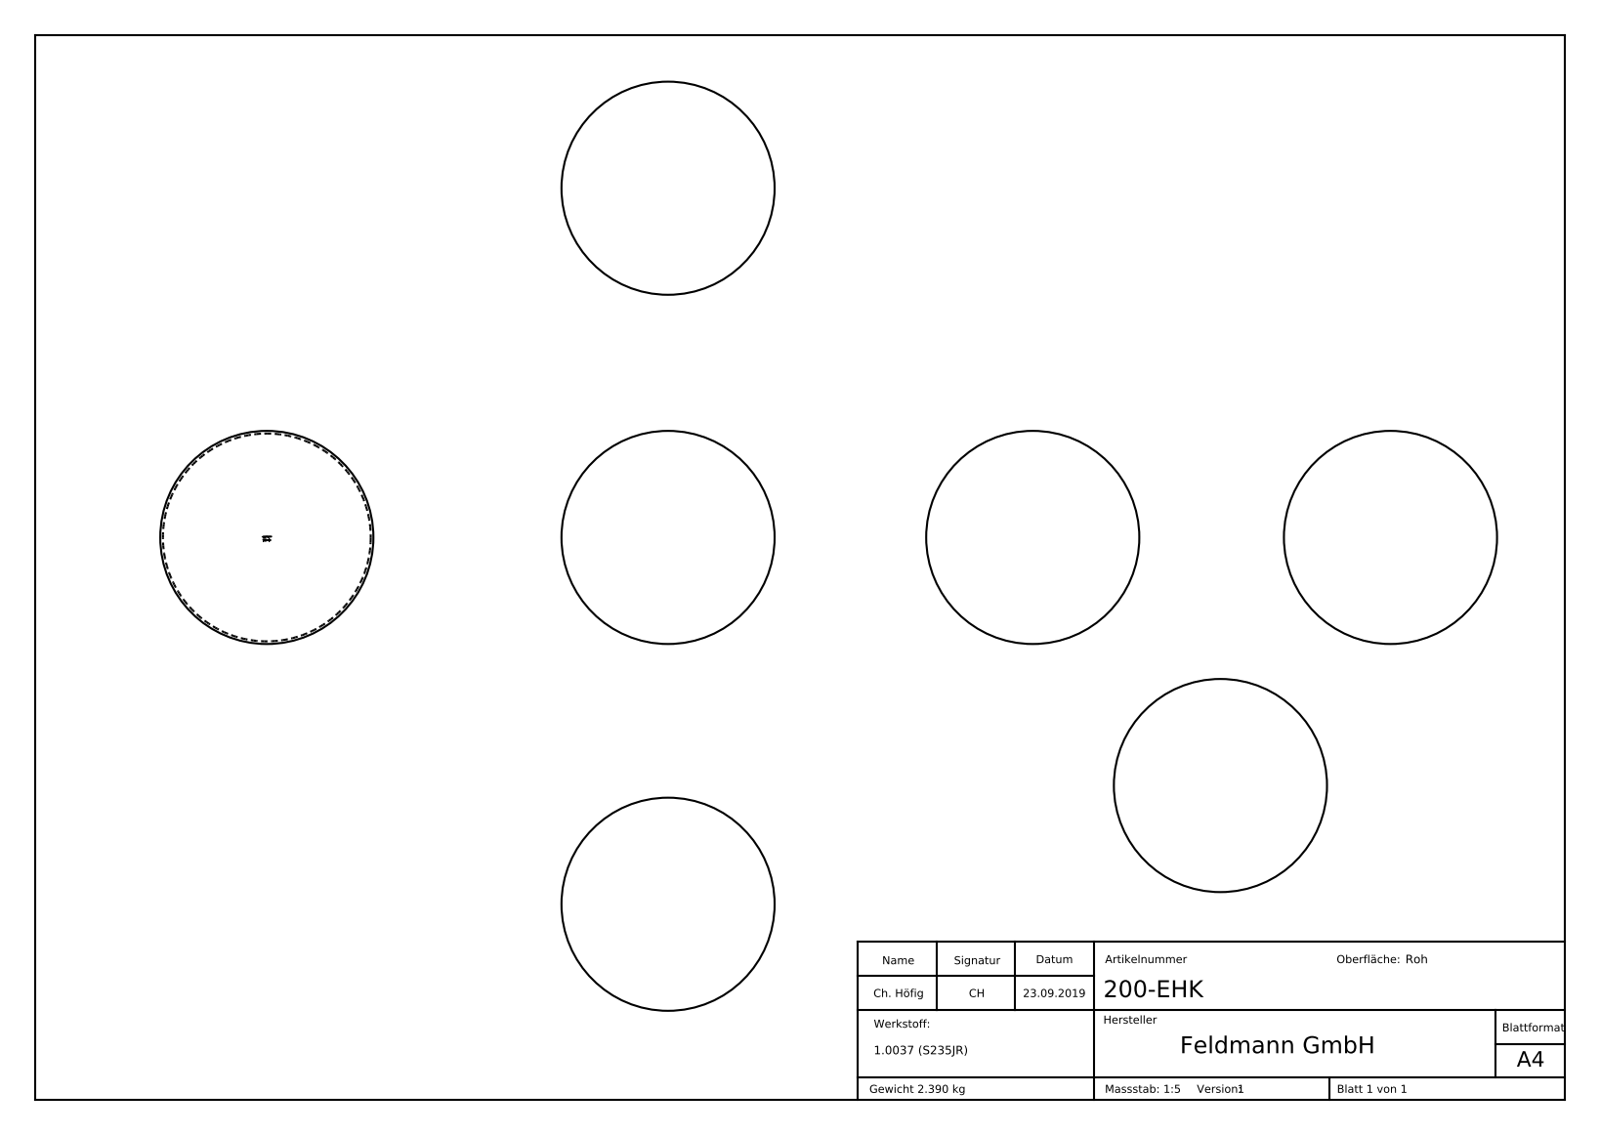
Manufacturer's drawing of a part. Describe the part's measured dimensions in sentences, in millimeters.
The part is named "200-EHK". Its 3-D file was written by "SolidWorks 2015 (CONFIG_CONTROL_DESIGN)". It is 1 solid with 197 faces: 99 planar, 0 cylindrical and 98 other. Overall it measures 200 by 200 by 200 millimeters. Its volume is 306 370 cubic millimeters and its surface area 245 132 square millimeters. The main face-to-face distances are 3.2, 1.26, 3.13, 4.5, 0.46, 1.35, 3.59, 0.68, 0.64, 3.47.
